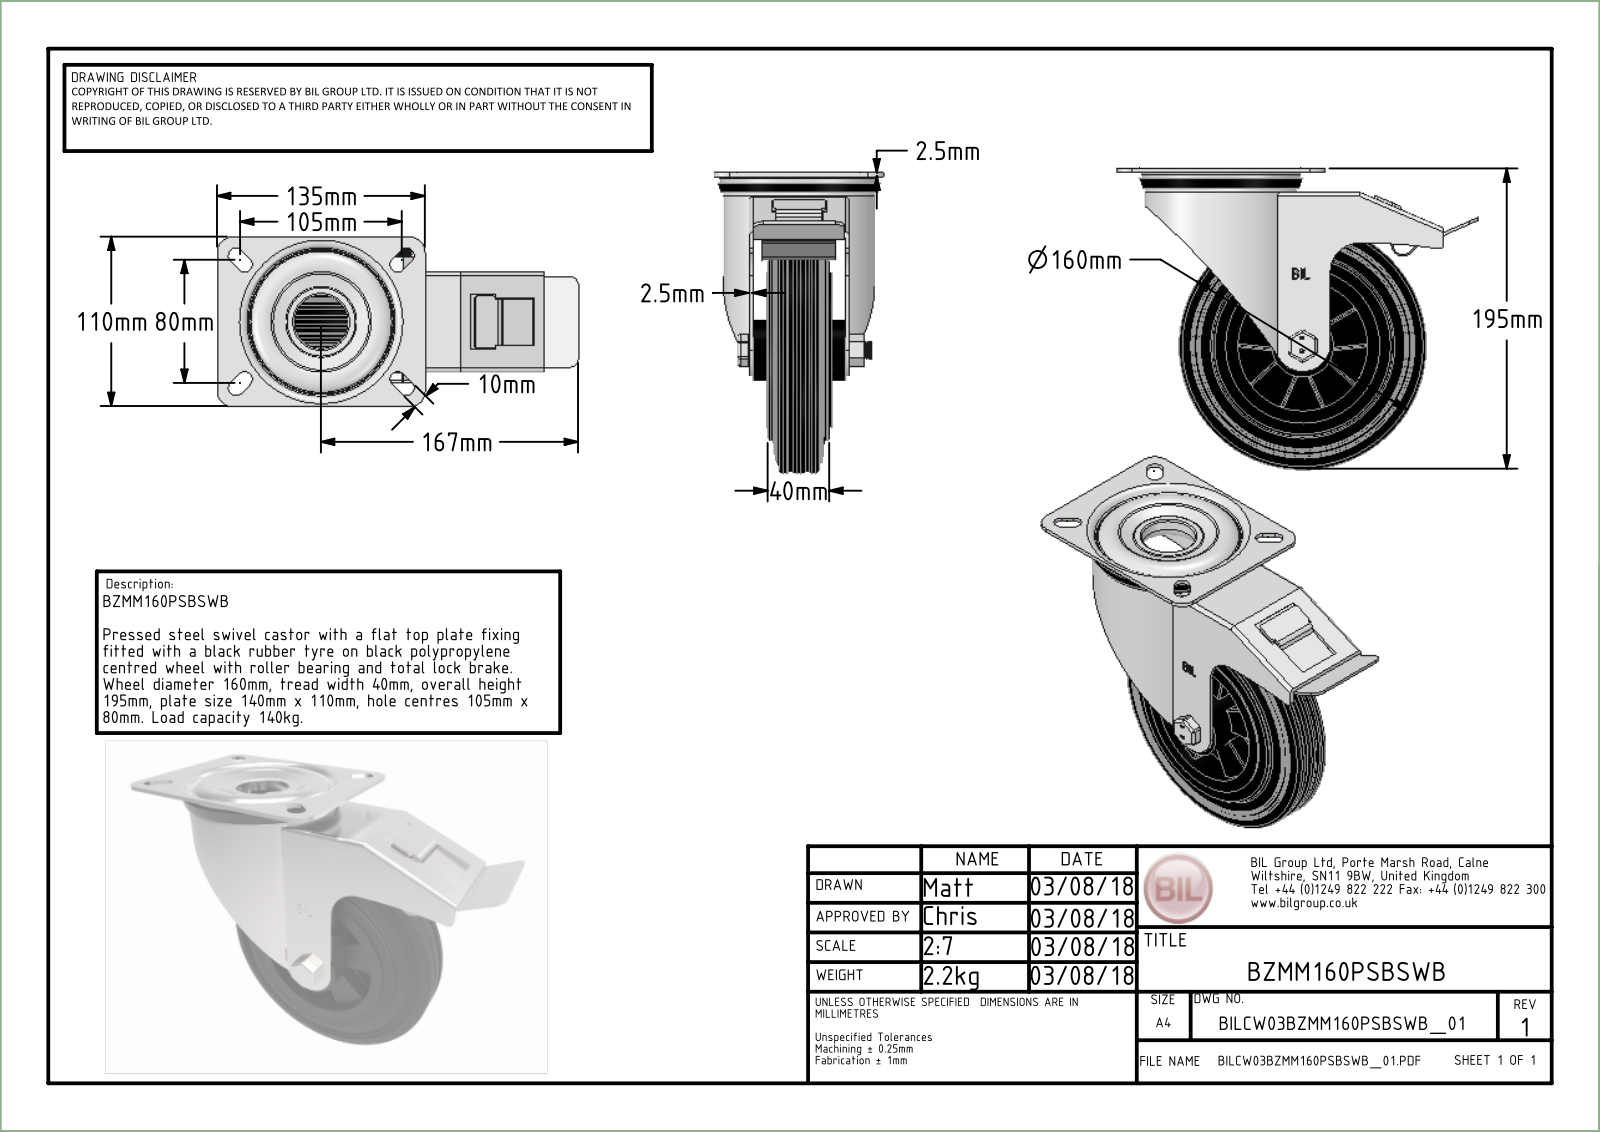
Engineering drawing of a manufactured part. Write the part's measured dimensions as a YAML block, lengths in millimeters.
part_name: "BZMM160PSBSWB v4; BZMM160ASSWB/LITE v2; ZINC PLATED, PRESSED STEEL TOP PLATE (1); ZINC PLATED, PRESSED STEEL TOP PLATE Geometry (1) (+8 more)"
step_written_by: "Autodesk Translation Framework v13.20.0.188 (AP242_MANAGED_MODEL_BASED_3D_ENGINEERING_MIM_LF)"
units: millimeters
bodies: {solids: 64, faces: 914, planar: 335, cylindrical: 210, other: 369}
overall_size: [234.5, 195, 110]
volume: 780609
surface_area: 291355
round_holes:
  - {diameter: 94, count: 2}
  - {diameter: 8, count: 1}
  - {diameter: 11, count: 1}
  - {diameter: 12, count: 1}
  - {diameter: 12.2, count: 1}
  - {diameter: 12.5, count: 1}
  - {diameter: 14, count: 1}
  - {diameter: 20, count: 1}
  - {diameter: 33.75, count: 1}
  - {diameter: 34, count: 1}
  - {diameter: 35, count: 1}
  - {diameter: 39.75, count: 1}
round_bosses_or_shafts:
  - {diameter: 7.5, count: 8}
  - {diameter: 158.4, count: 1}
  - {diameter: 109, count: 1}
  - {diameter: 101, count: 1}
  - {diameter: 98, count: 1}
  - {diameter: 78, count: 1}
  - {diameter: 50, count: 1}
  - {diameter: 40, count: 1}
partial_cylinders:
  - {radius: 0.5, count: 18}
  - {radius: 1, count: 12}
  - {radius: 1.5, count: 10}
  - {radius: 5.5, count: 10}
  - {radius: 0.25, count: 6}
  - {radius: 2.5, count: 6}
  - {radius: 3, count: 6}
  - {radius: 10, count: 4}
face_to_face_distances: [2.5, 9, 5, 62.5, 1, 13, 6.5, 15.5, 4, 18]
hole_center_spacings: [67]
